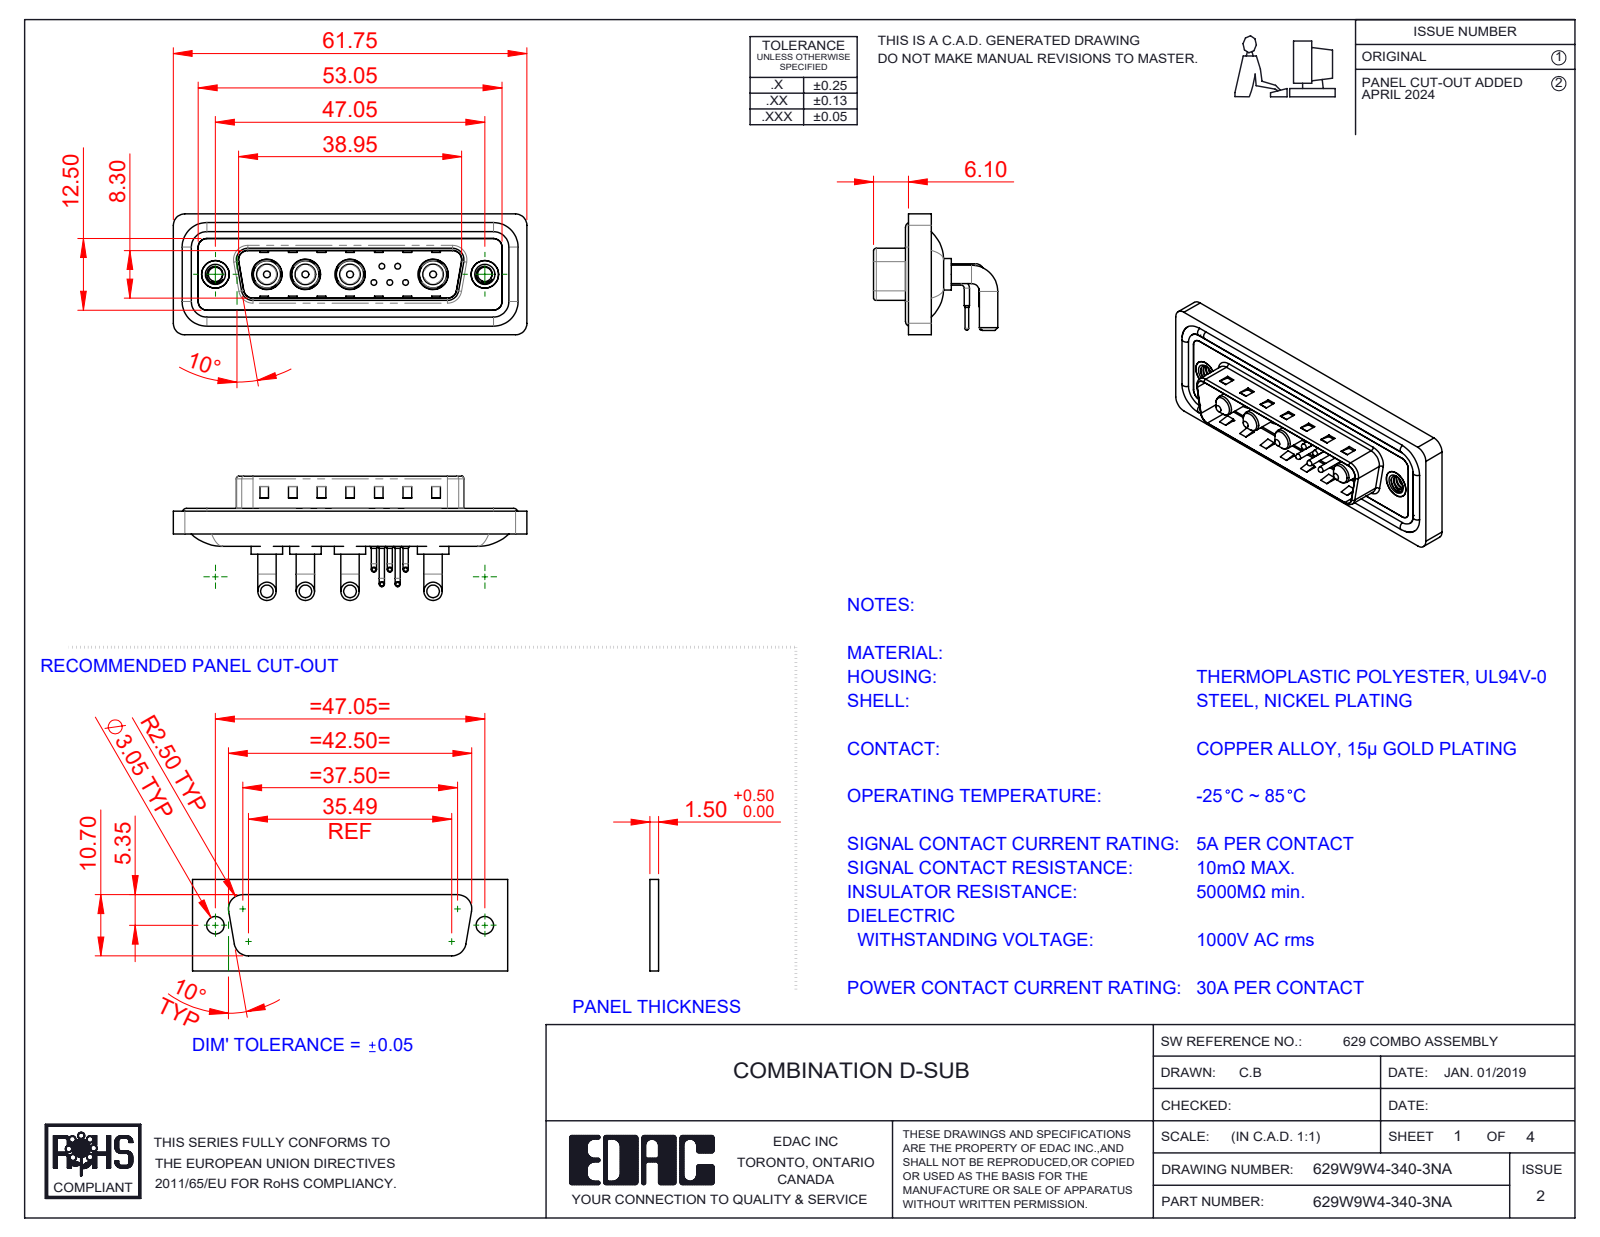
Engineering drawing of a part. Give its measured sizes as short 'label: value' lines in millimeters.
name: 629Combo Contact Row 1; Power Pin_30A RA; 629Combo Housing_9W4; 629Combo Threaded Rivet_A (+5 more)
written by: SolidWorks 2023 (CONFIG_CONTROL_DESIGN)
unit: mm
bodies: 20 solids, 1199 faces (569 planar, 450 cylindrical, 180 other)
size: 61.75 × 21.7 × 21.1
volume: 7 820 mm³; area: 12 454 mm²
holes: 5× ⌀0.75, 5× ⌀1.6, 5× ⌀2, 4× ⌀4.85, 4× ⌀5.3, 2× ⌀2.5, 2× ⌀4, 2× ⌀4.8, 2× ⌀5
bosses: 10× ⌀0.9, 8× ⌀3.2, 5× ⌀1.5, 5× ⌀1, 5× ⌀0.65, 4× ⌀5.5, 4× ⌀5.2, 4× ⌀4.75
rounds: 18× R1.5, 18× R2, 8× R0.5, 8× R1.6, 5× R1.01, 4× R0.25, 4× R0.6, 4× R0.65
face distances: 0.4, 2.9, 0.8, 4.1, 1.1, 4.5, 2.1, 1.6, 3.1, 1.5
hole spacings: 3.16, 2.77, 5.04, 14.5, 2.78, 4.4, 4.41, 5
